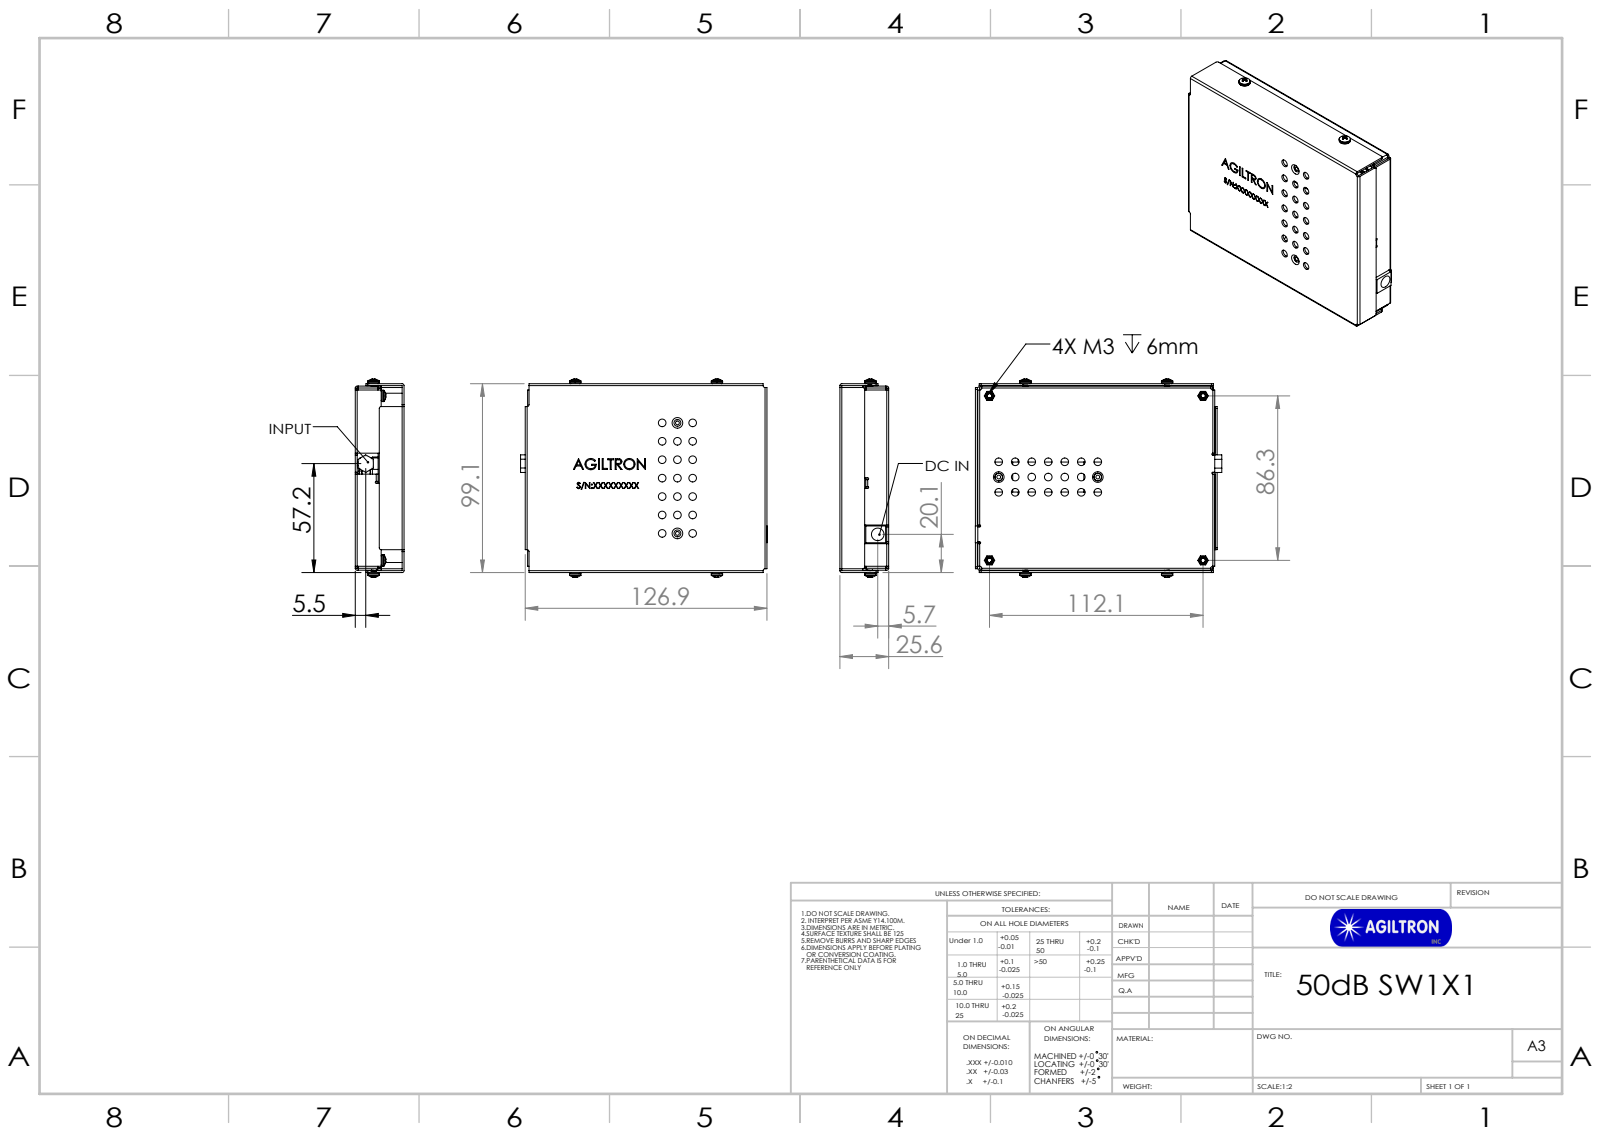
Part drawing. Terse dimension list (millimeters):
name: S-M2,5-1; 50dB SW1X1; 1001857_BOTTOM ASM; BOTTOM COVER BRIDGE (+8 more)
written by: SolidWorks 2017 (CONFIG_CONTROL_DESIGN)
unit: mm
bodies: 21 solids, 966 faces (439 planar, 275 cylindrical, 252 other)
size: 129.4 × 103.99 × 25.6
volume: 73 260 mm³; area: 110 249 mm²
holes: 40× ⌀4, 8× ⌀4.2, 6× ⌀2.55, 4× ⌀2, 4× ⌀3.5, 1× ⌀6.6
bosses: 6× ⌀3, 4× ⌀6.3, 4× ⌀4.19, 4× ⌀3.59, 2× ⌀3.55, 1× ⌀6
rounds: 96× R0.29, 38× R1, 11× R0.5, 8× R0.2, 8× R1.2, 8× R2, 4× R1.6
face distances: 1, 24.6, 11, 12, 12.6, 13.6, 23.6, 25.6, 1.6, 1.25
hole spacings: 20.92, 8, 12.55, 30.08, 9.67, 19.33, 29, 12.54
